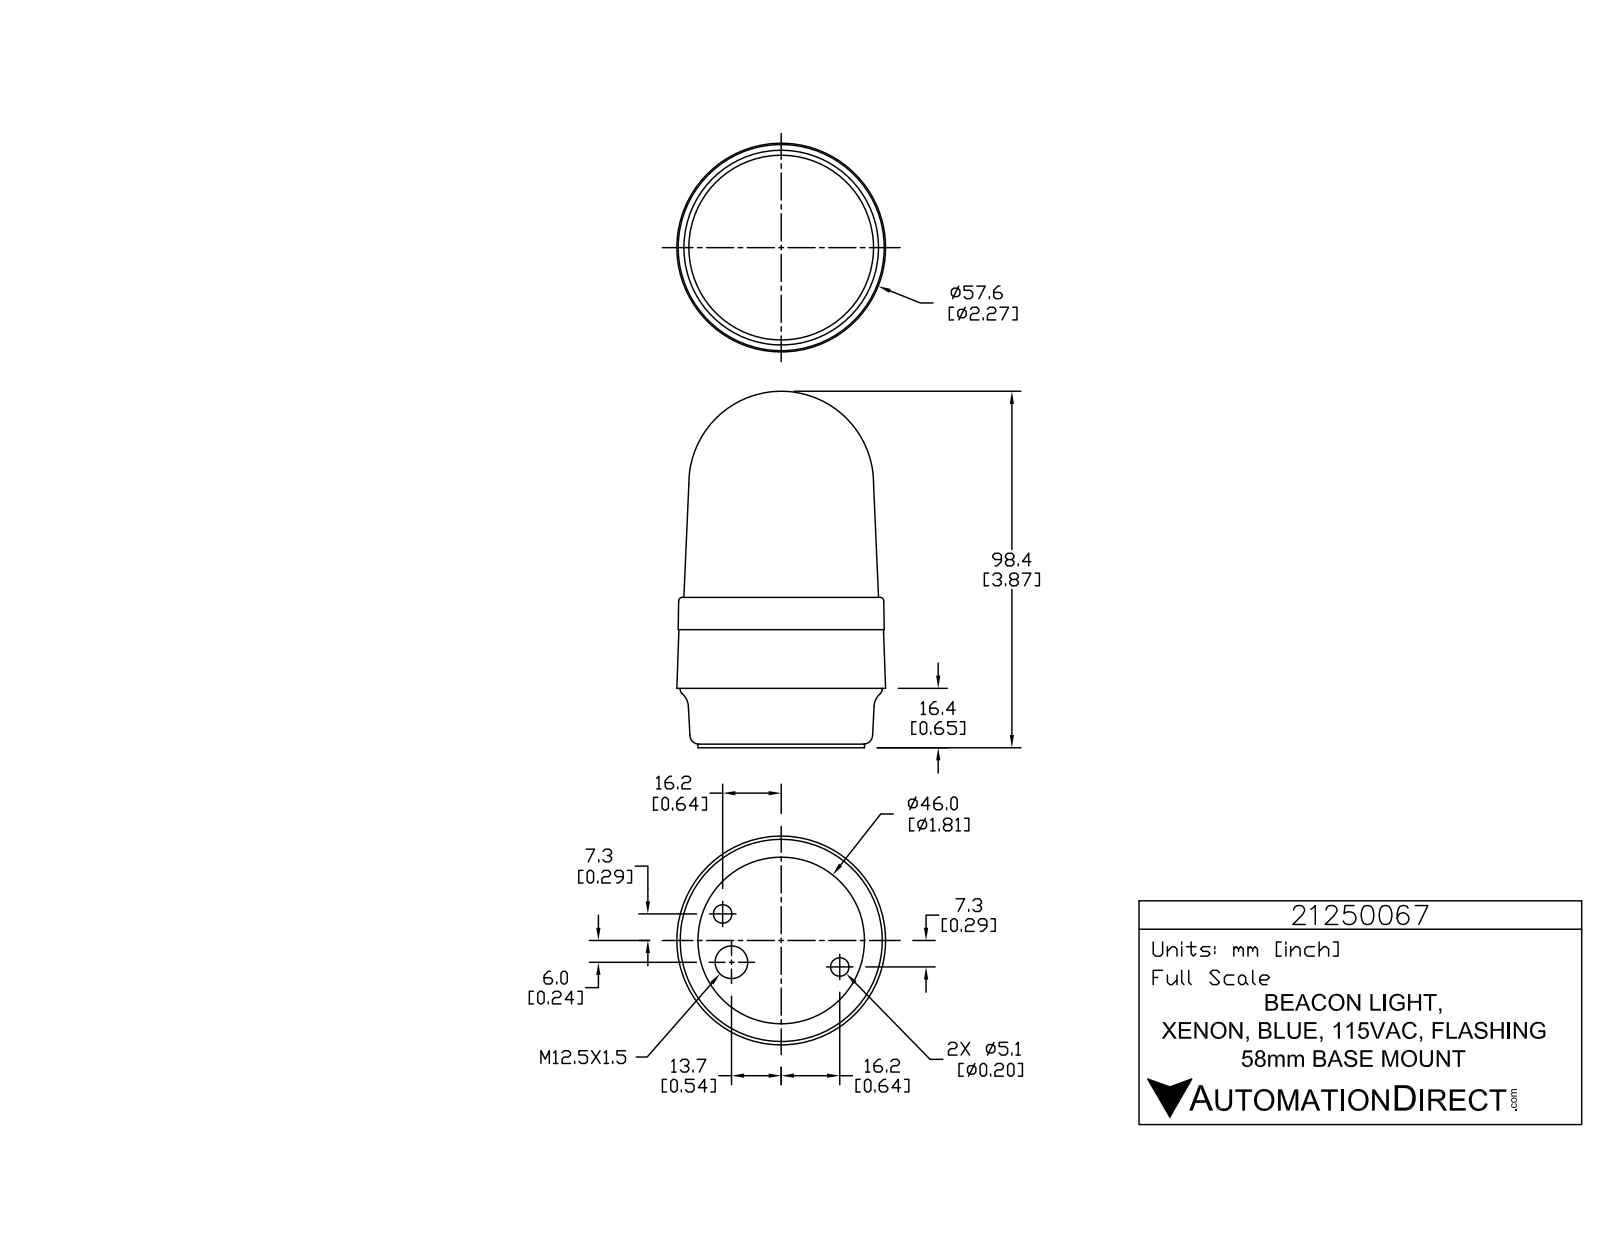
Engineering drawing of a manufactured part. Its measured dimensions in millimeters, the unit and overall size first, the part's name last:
Units: millimetres
Overall size (bounding box): 98.4 × 57.63 × 57.63
Round holes (diameter × count): ⌀0.99 ×3, ⌀5.11 ×2, ⌀9 ×1
Round bosses / shafts (diameter × count): ⌀5.74 ×3, ⌀1.43 ×3, ⌀55.8 ×1, ⌀46 ×1
Partial cylindrical surfaces — rounded edges, fillets, slot ends (radius × count): R0.2 ×6, R0.21 ×6, R0.21 ×6, R3.32 ×6, R0.1 ×3, R0.12 ×3, R0.19 ×3, R0.2 ×3
Main face-to-face distances: 16.4, 1, 15.4, 41.5, 40.5, 25.1, 32.6, 31.6, 16.2, 8.9
Hole centre spacings: 13.56, 29.94, 35.5
Volume: 199 898 mm³ · Surface area: 18 922 mm²
Bodies: 1 solid, 764 faces (527 planar, 145 cylindrical, 92 other)
Part name (STEP PRODUCT): 21250067
STEP written by: SolidWorks 2015 (AUTOMOTIVE_DESIGN)
